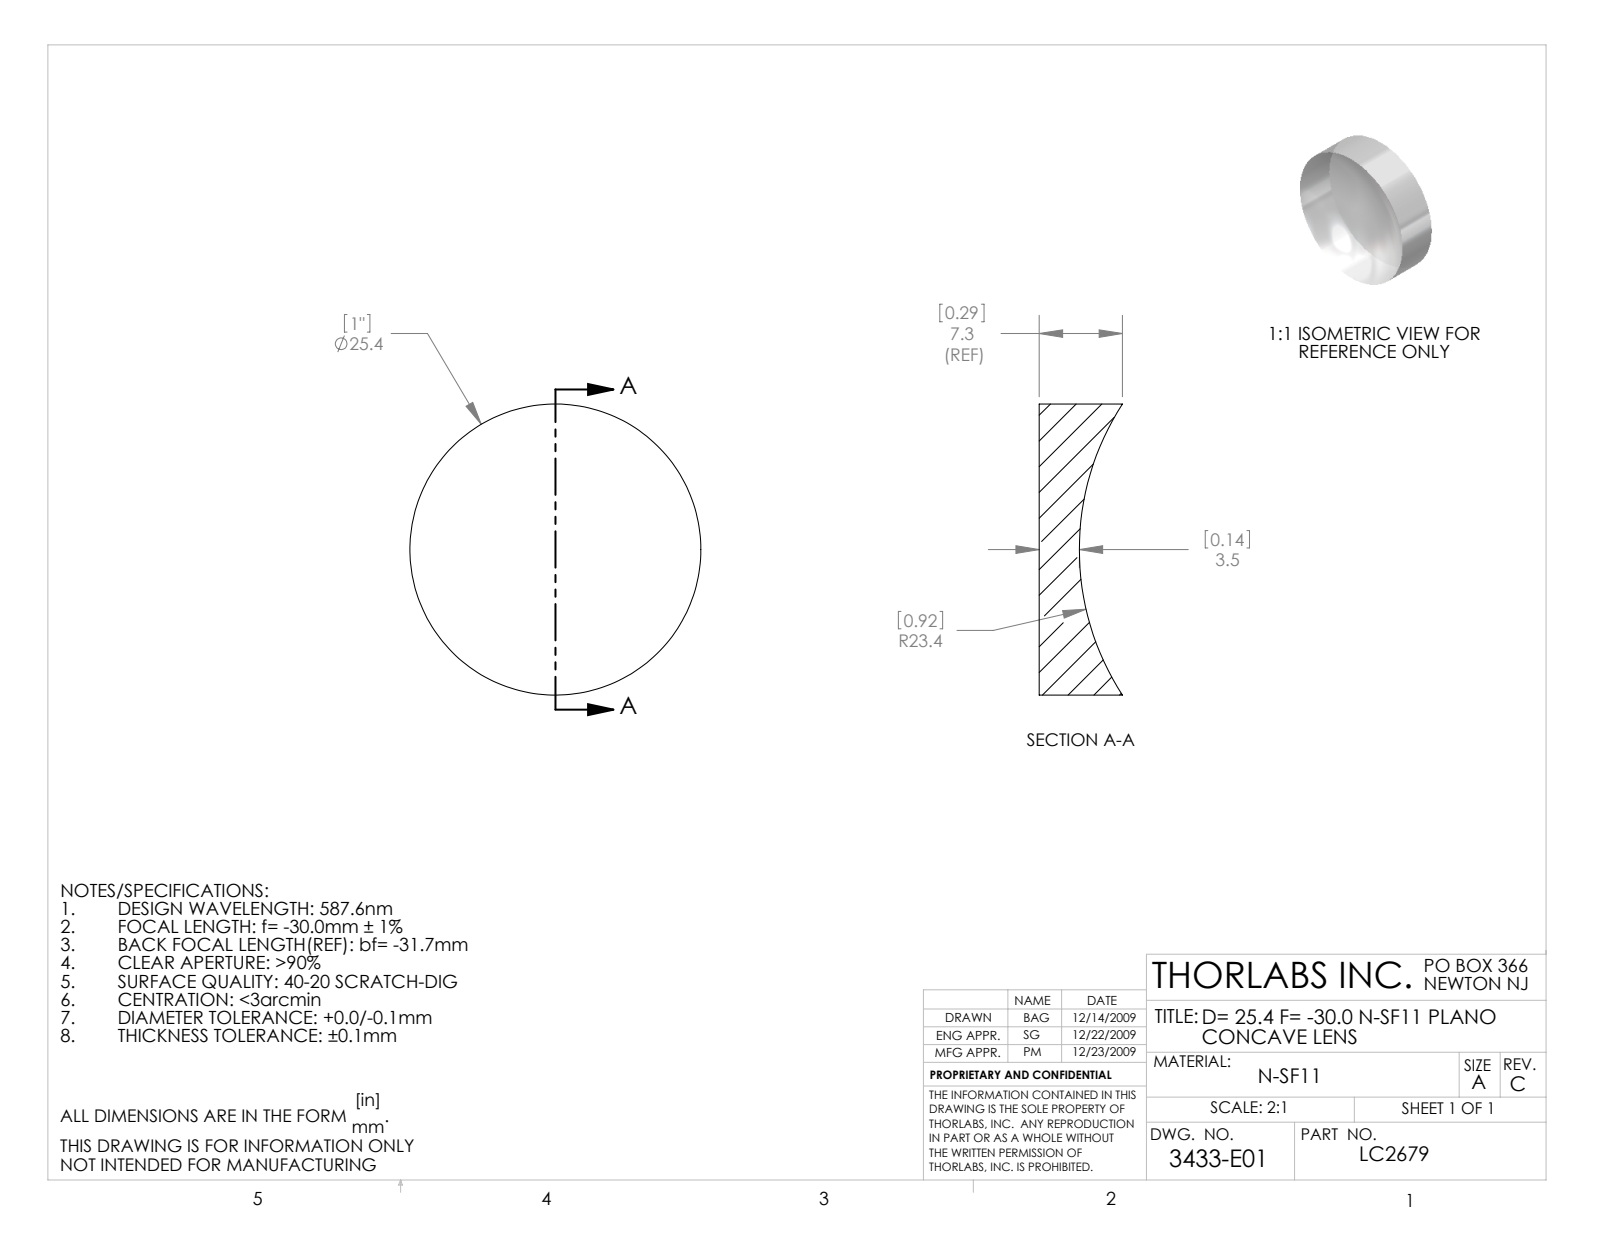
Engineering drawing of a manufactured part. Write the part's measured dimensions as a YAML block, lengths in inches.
part_name: "3433-E0W"
step_written_by: "SolidWorks 2009 (AUTOMOTIVE_DESIGN)"
units: inches
bodies: {solids: 1, faces: 5, planar: 1, cylindrical: 2, other: 2}
overall_size: [1, 1, 0.286]
volume: 0.165
surface_area: 2.537
round_bosses_or_shafts:
  - {diameter: 1, count: 1}
